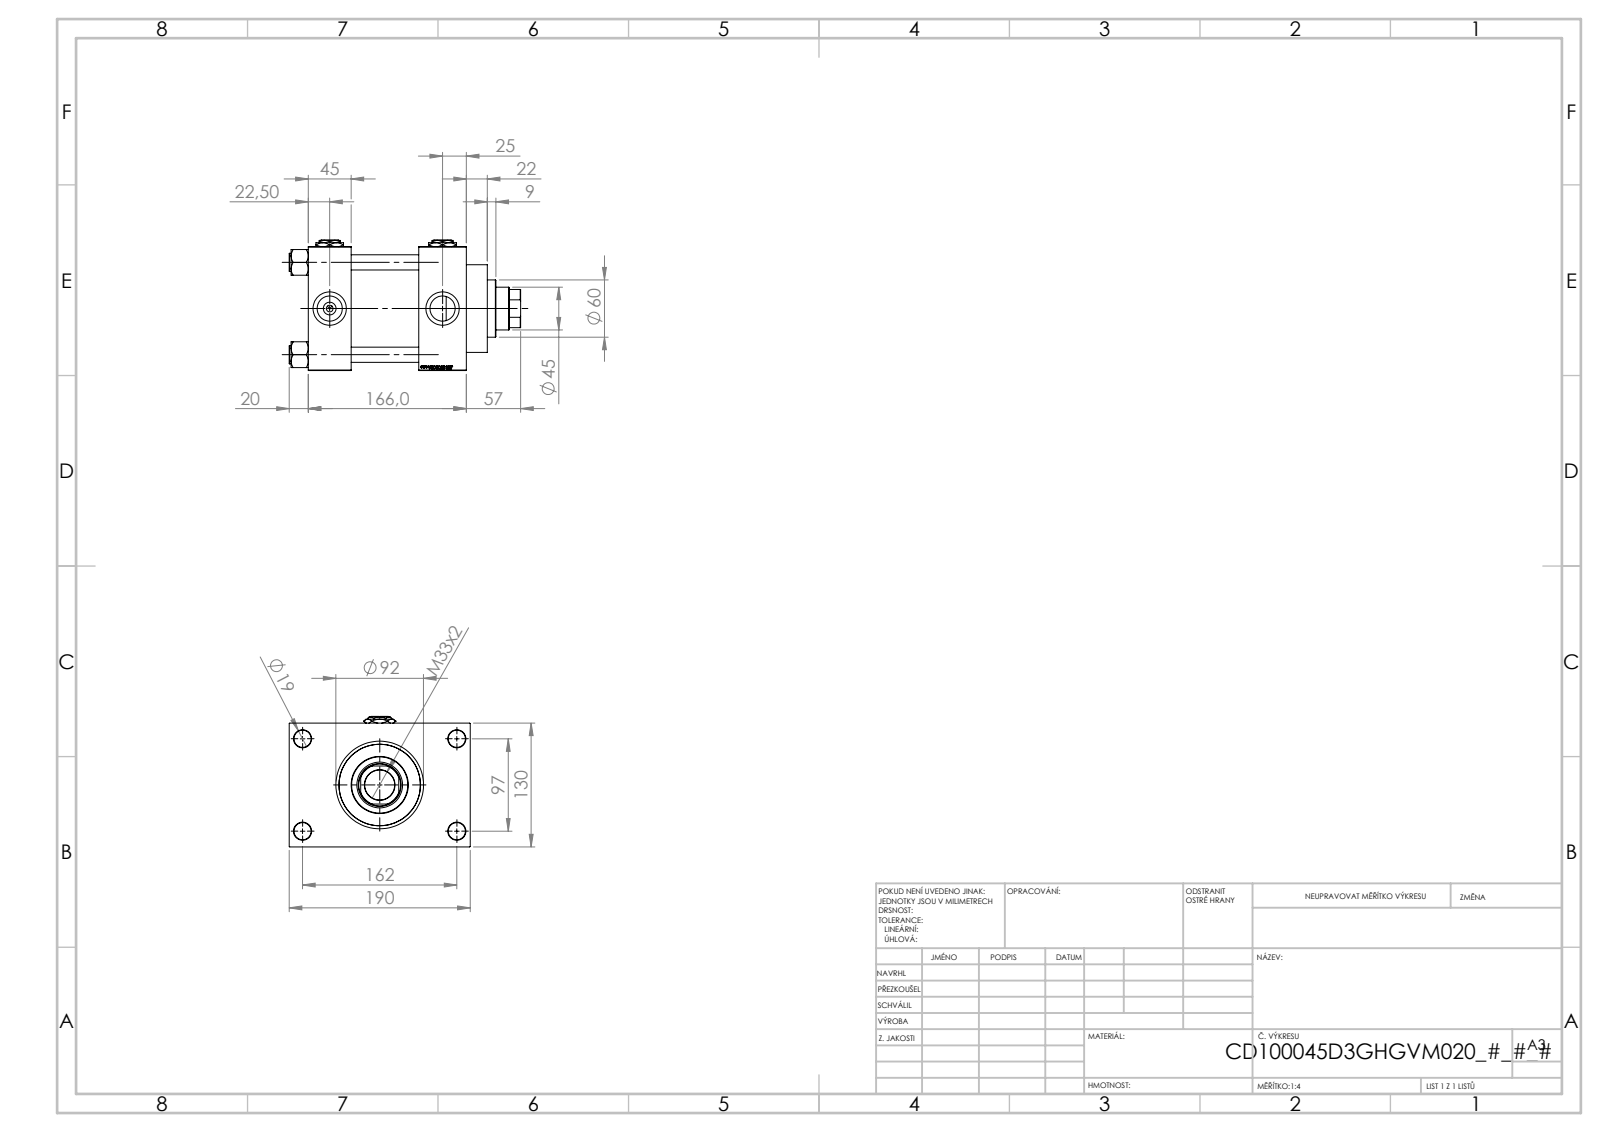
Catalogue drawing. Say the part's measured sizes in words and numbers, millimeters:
The part is named "V215CD_D_Body; V215CD_D_TYCINKA; V215CD_VC_A; V215CD_VCP_D (+2 more)". Its 3-D file was written by "SolidWorks 2019 (CONFIG_CONTROL_DESIGN)". It is 13 solids with 1252 faces: 593 planar, 99 cylindrical and 560 other. Overall it measures 243 by 190 by 137 millimeters. Its volume is 2 576 000 cubic millimeters and its surface area 361 795 square millimeters. Round holes: 4 of diameter 16, 4 of diameter 18, 4 of diameter 26.44, 4 of diameter 35, 3 of diameter 7, 1 of diameter 31.5, 1 of diameter 45, 1 of diameter 48, 1 of diameter 76, 1 of diameter 85.5, 1 of diameter 100. Round bosses or shafts: 4 of diameter 19, 1 of diameter 106, 1 of diameter 92, 1 of diameter 60. Partial cylindrical surfaces (rounded edges, fillets, slot ends): 1 of radius 22. The main face-to-face distances are 45, 130, 116, 71, 166, 121, 50, 30, 160, 20. The hole center spacings are 32.55, 68.52, 94.41, 96.9, 102.27, 129.45, 161.73, 97.
